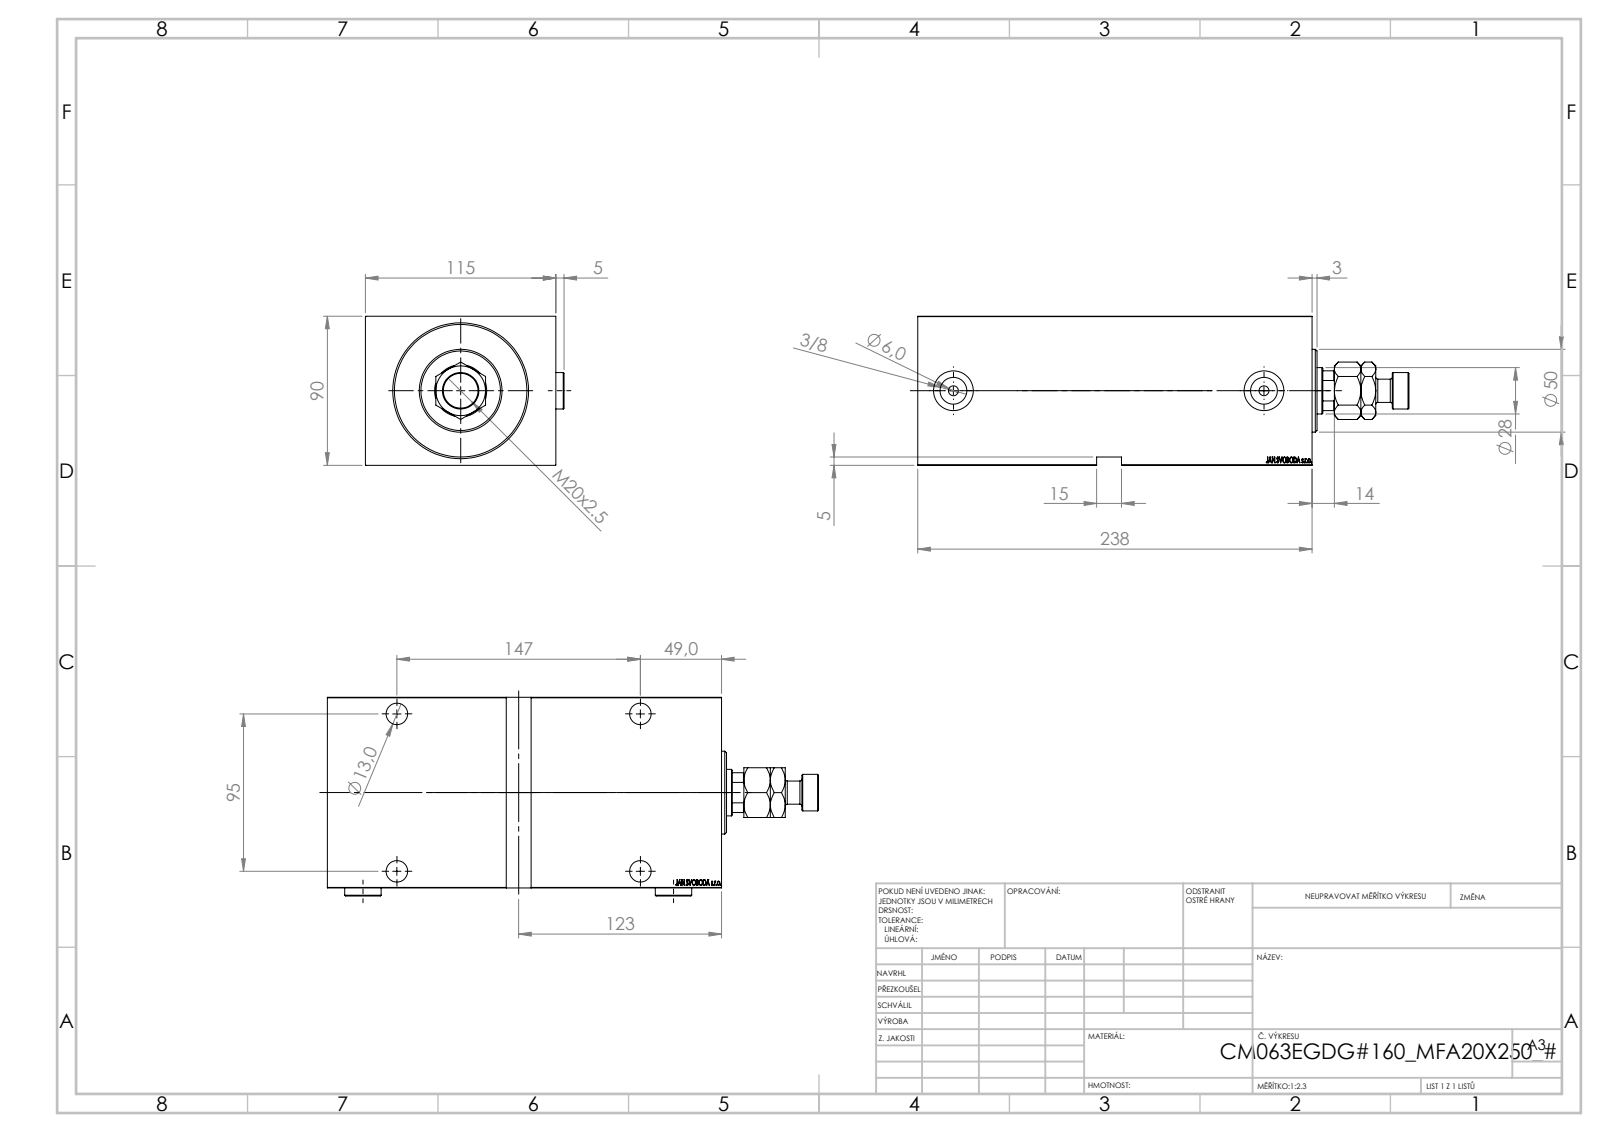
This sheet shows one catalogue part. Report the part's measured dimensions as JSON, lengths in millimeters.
{"part_name": "V450CM_VC_B; MFA; Zatka_OIL_PORT; V450CM_E_Body (+1 more)", "step_written_by": "SolidWorks 2019 (CONFIG_CONTROL_DESIGN)", "units": "millimeters", "bodies": {"solids": 6, "faces": 964, "planar": 462, "cylindrical": 72, "other": 430}, "overall_size": [296.5, 119.9, 90], "volume_mm3": 2022000, "surface_area_mm2": 237690, "round_holes": [[13, 4], [19, 4], [6, 2], [16.17, 2], [24, 2], [18.5, 1], [28, 1], [31.5, 1], [63, 1], [80, 1]], "round_bosses_or_shafts": [[22, 3], [65, 1], [50, 1], [14, 1]], "partial_cylinders_radius": [[13.5, 1]], "face_to_face_distances": [90, 115, 238, 17.5, 220.5, 5, 233, 215.5, 168.5, 173.5], "hole_center_spacings": [95, 147, 175.03, 187.5]}
